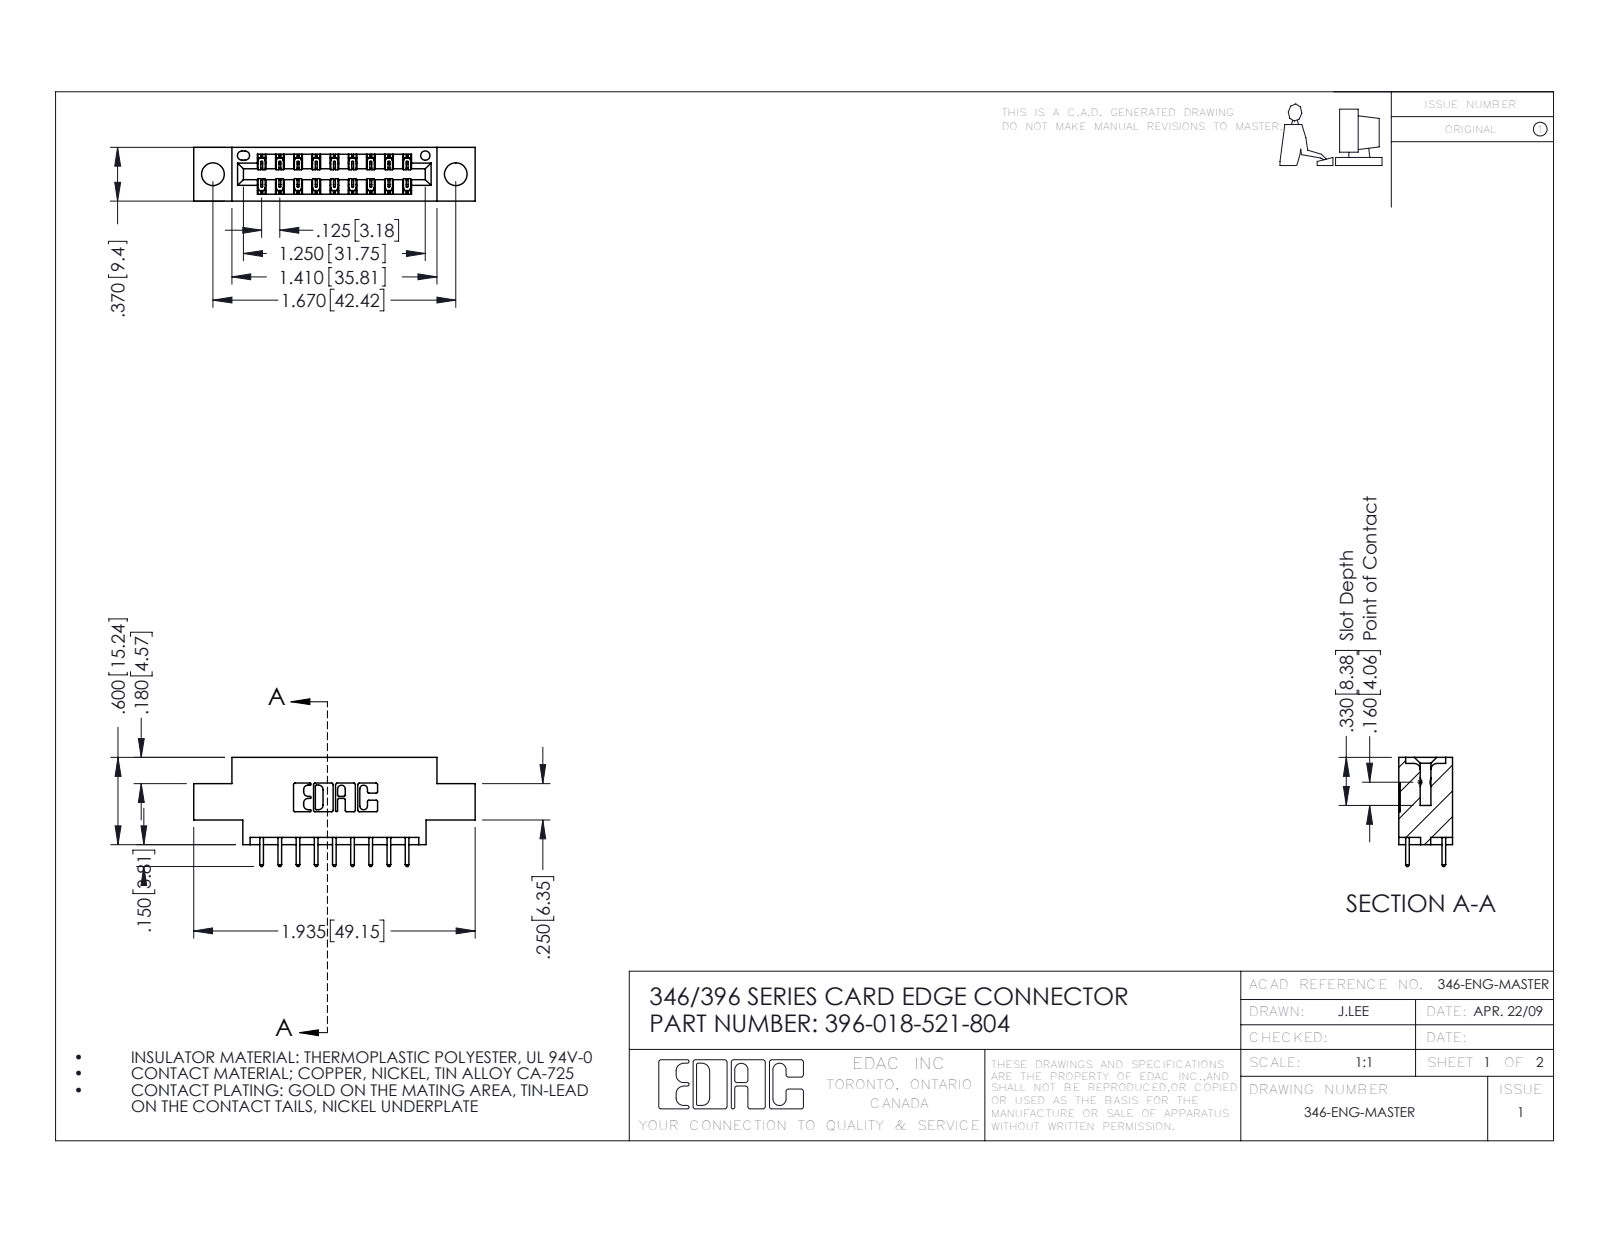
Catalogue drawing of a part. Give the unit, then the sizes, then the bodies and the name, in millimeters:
Units: millimetres
Overall size (bounding box): 49.1 × 19.1 × 9.4
Round holes (diameter × count): ⌀4 ×2, ⌀1.6 ×1
Partial cylindrical surfaces — rounded edges, fillets, slot ends (radius × count): R0.2 ×27, R0.3 ×22, R0.3 ×18, R0.2 ×6, R0.8 ×6, R0.7 ×3, R0.4 ×2, R0.6 ×2
Main face-to-face distances: 6.4, 9.4, 1.2, 8.2, 1.8, 7.6, 0.6, 7, 3.8, 5.6
Hole centre spacings: 6.2, 37.2, 42.4
Volume: 4 290 mm³ · Surface area: 5 317 mm²
Bodies: 19 solids, 1062 faces (710 planar, 352 cylindrical, 0 other)
Part name (STEP PRODUCT): 396-018-521-804; 346 Part_0.170 Offset - 0.156 Dia-TH; 345-292-001_345-293-121
STEP written by: SolidWorks 2016 (CONFIG_CONTROL_DESIGN)
